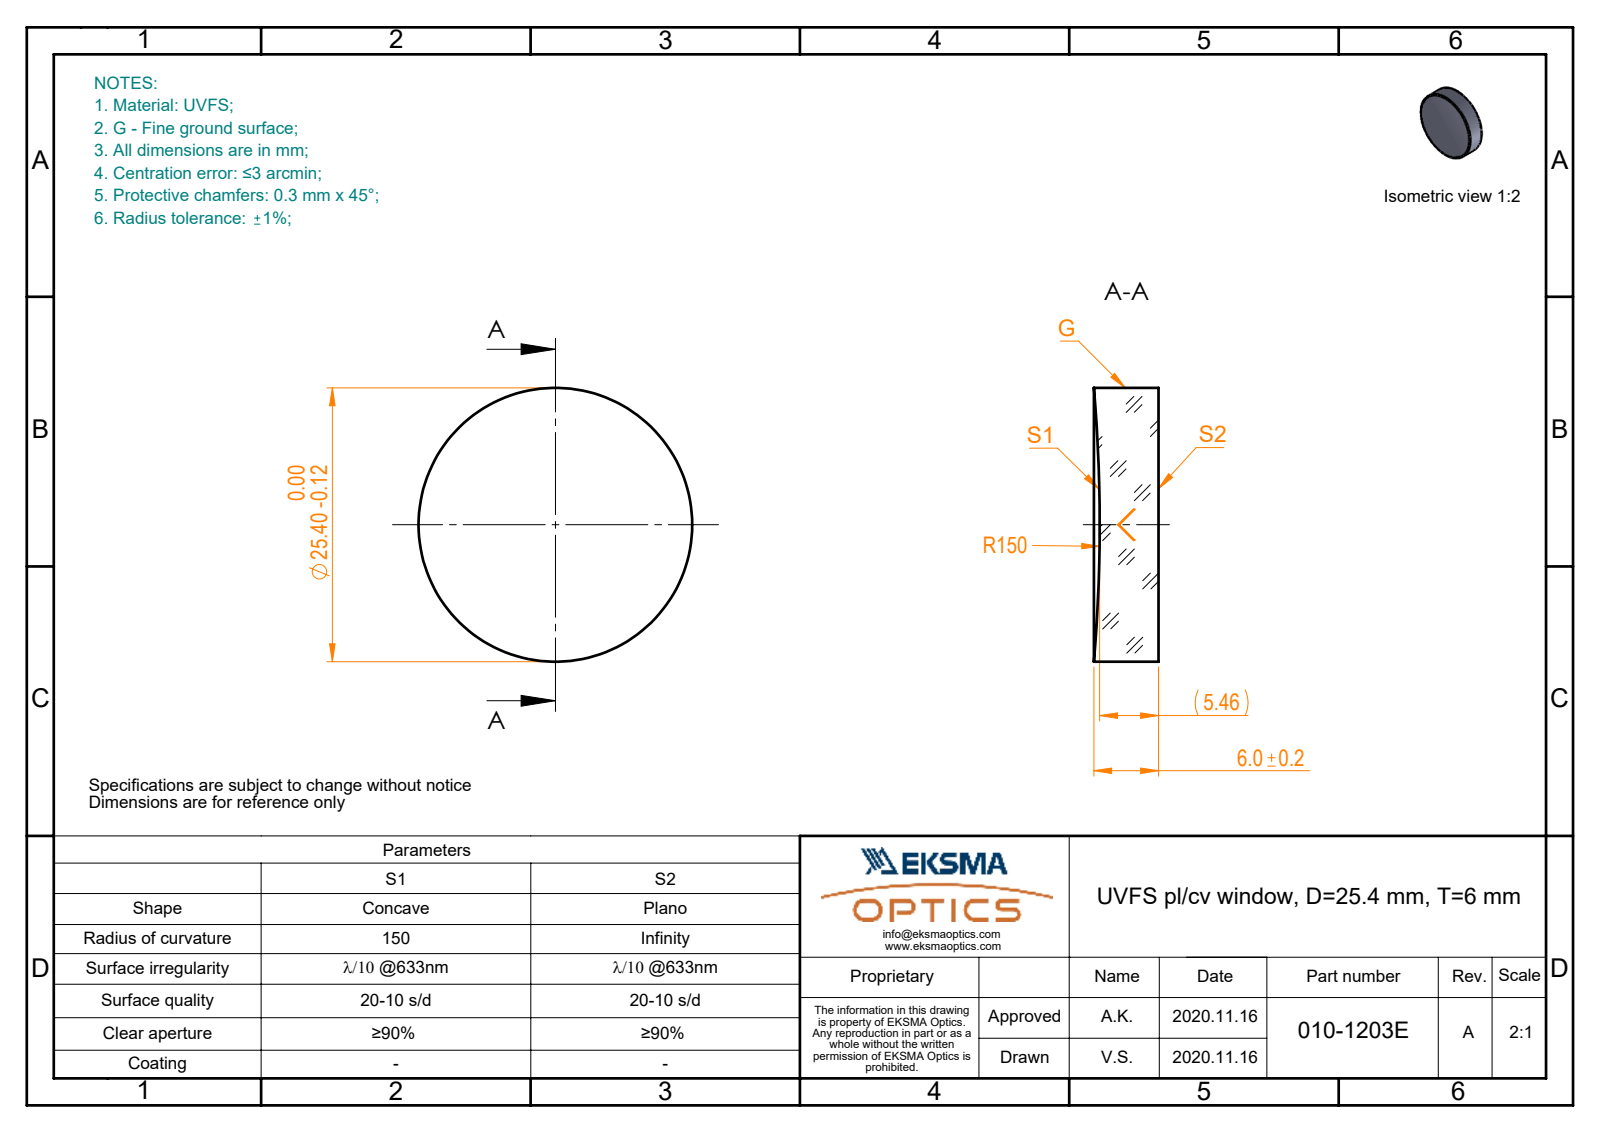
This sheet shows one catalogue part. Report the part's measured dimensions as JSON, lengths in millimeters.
{"part_name": "010-1203E_UVFS_PCV_window", "step_written_by": "SolidWorks 2019 (CONFIG_CONTROL_DESIGN)", "units": "millimeters", "bodies": {"solids": 1, "faces": 5, "planar": 1, "cylindrical": 2, "other": 2}, "overall_size": [25.4, 25.4, 6], "volume_mm3": 2904, "surface_area_mm2": 1493, "round_bosses_or_shafts": [[25.4, 1]]}
